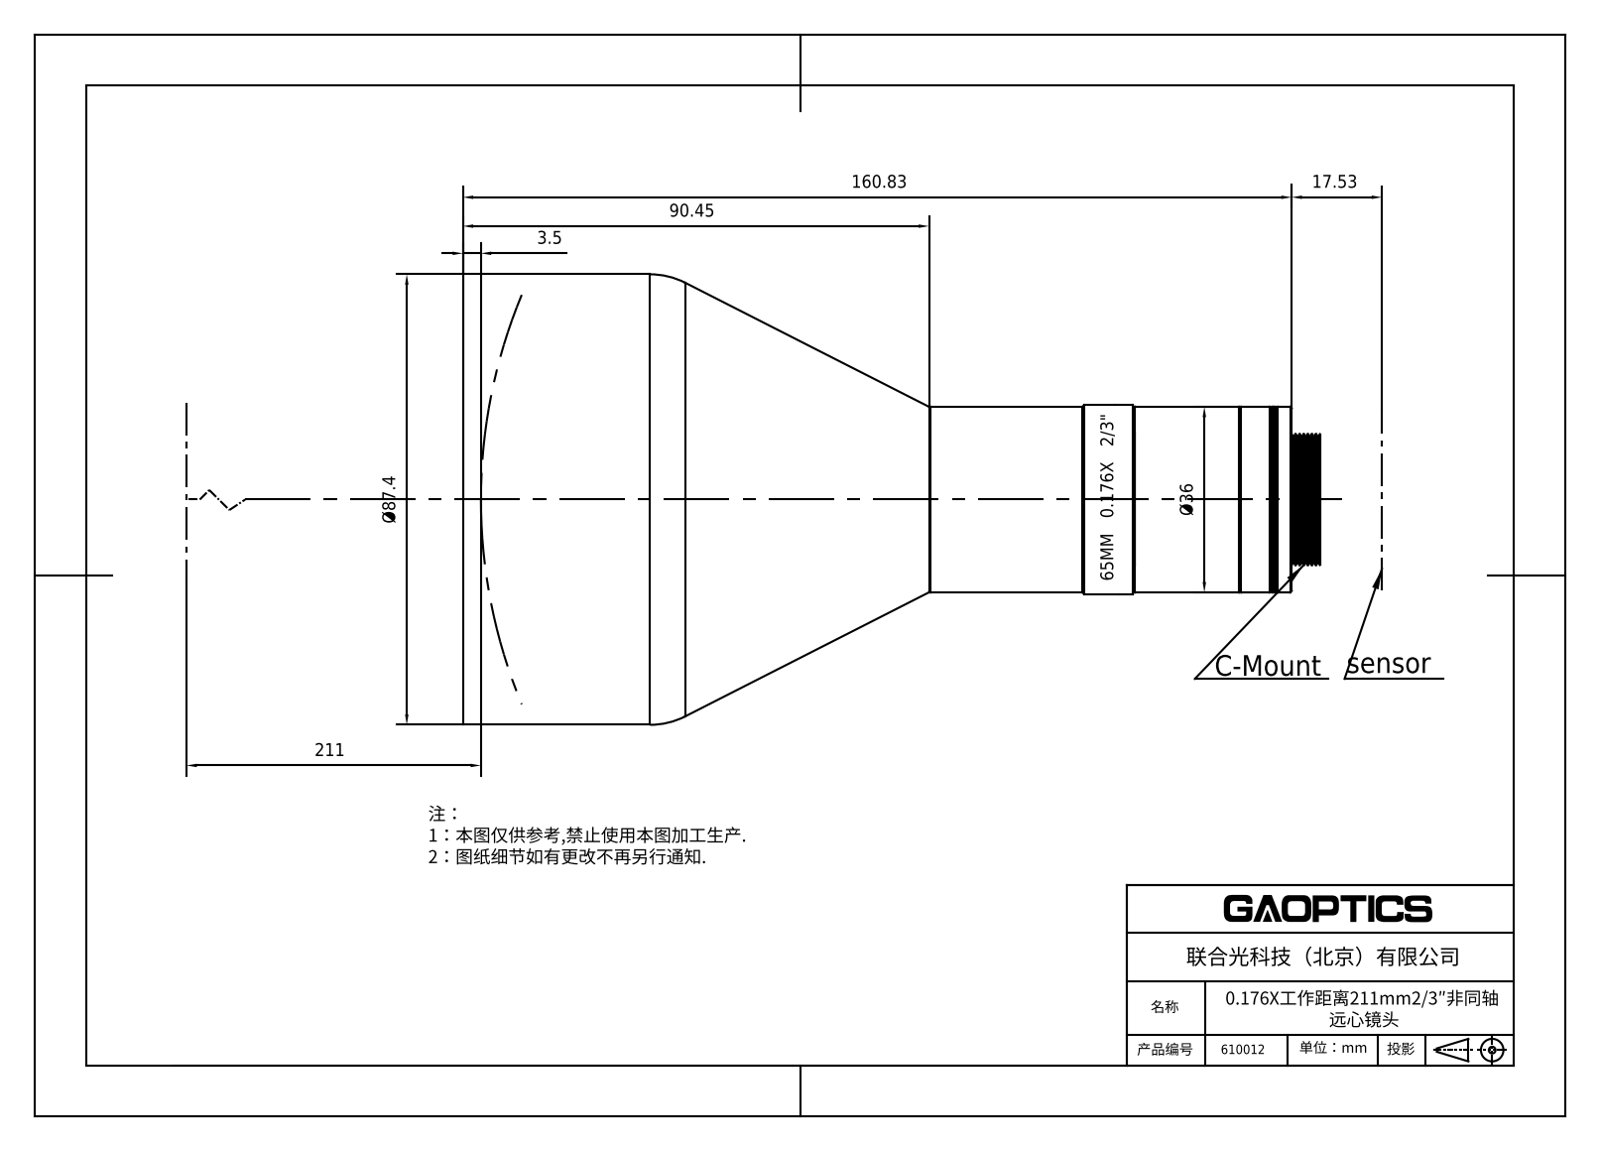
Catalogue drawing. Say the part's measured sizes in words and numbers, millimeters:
The part is named "610012". Its 3-D file was written by "SolidWorks 2020 (CONFIG_CONTROL_DESIGN)". It is 0 solids with 218 faces: 26 planar, 98 cylindrical and 94 other. Overall it measures 166.18 by 87.4 by 87.4 millimeters. Round holes: 1 of diameter 16.5, 1 of diameter 18.9, 1 of diameter 24.3, 1 of diameter 24.54, 1 of diameter 24.6, 1 of diameter 25.4, 1 of diameter 25.8, 1 of diameter 36, 1 of diameter 76.4, 1 of diameter 87.4. Round bosses or shafts: 3 of diameter 3, 3 of diameter 2.2, 1 of diameter 83.3, 1 of diameter 82, 1 of diameter 80.4, 1 of diameter 37, 1 of diameter 35, 1 of diameter 33. The main face-to-face distances are 1.2, 32.23, 33.43, 6, 109.63, 77.4, 76.2, 119.83, 87.6, 86.4.
